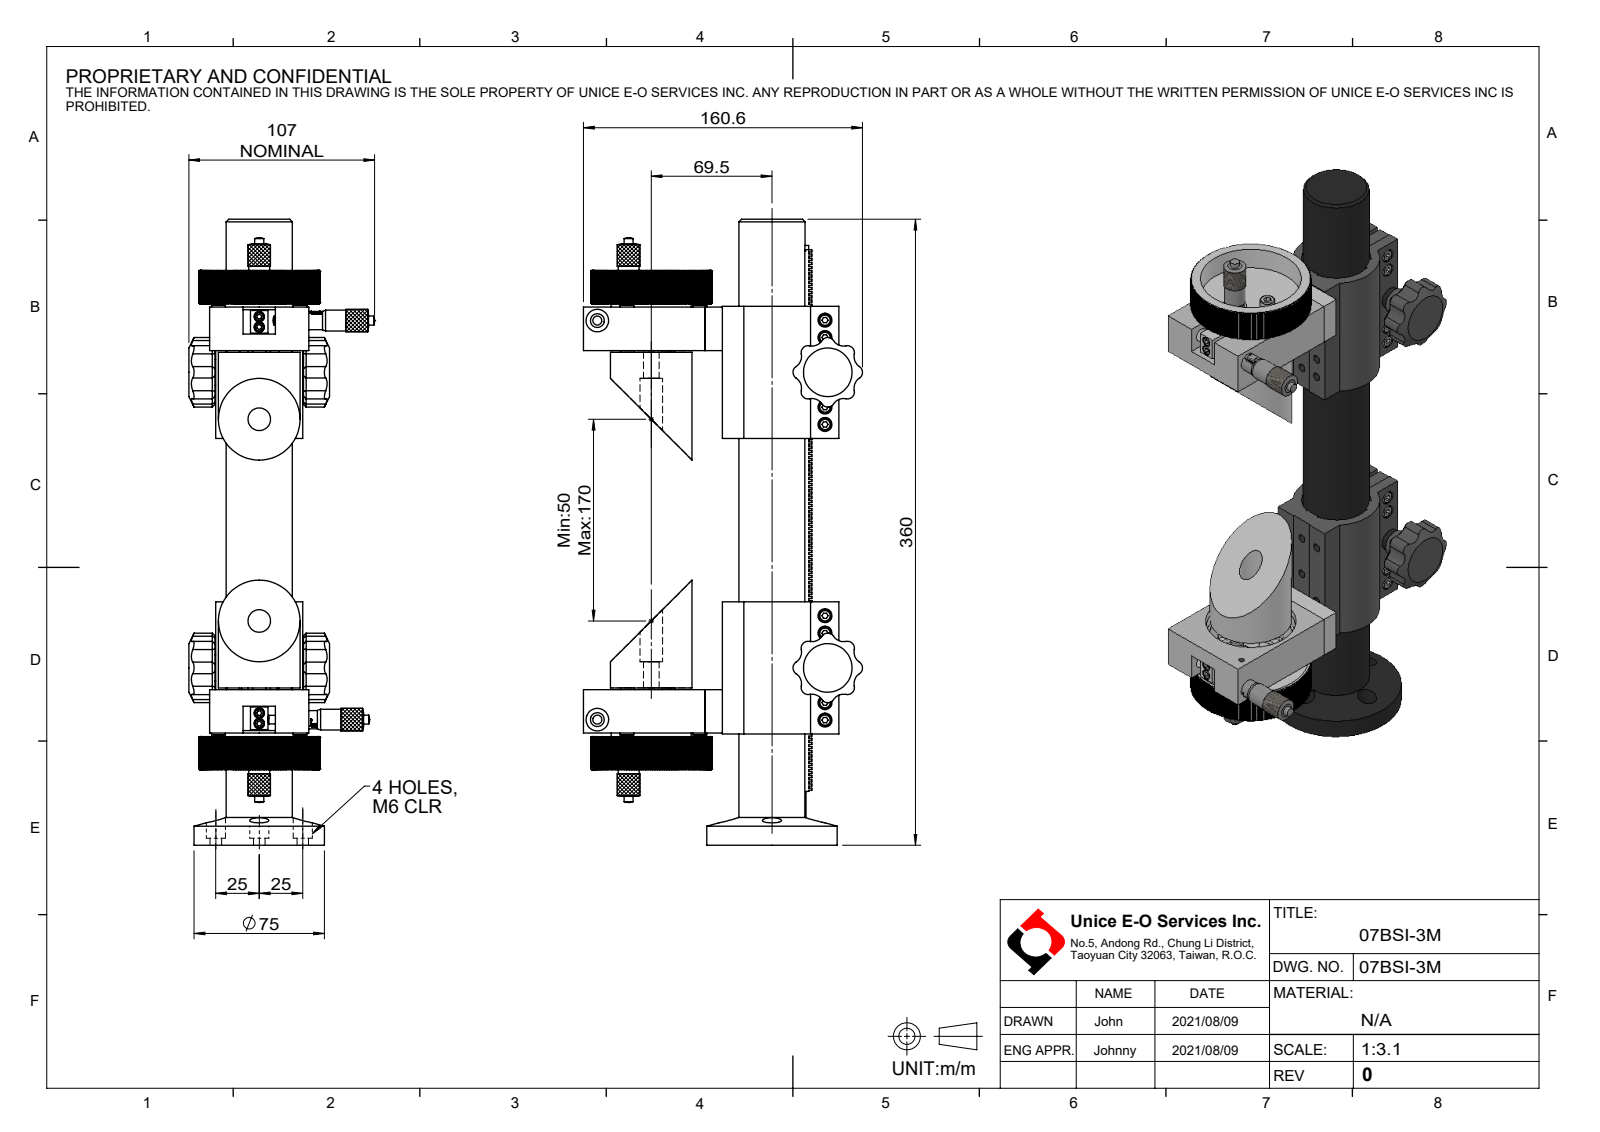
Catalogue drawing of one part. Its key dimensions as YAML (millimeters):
part_name: "07BSI-3M"
step_written_by: "SolidWorks 2020 (CONFIG_CONTROL_DESIGN)"
units: millimeters
bodies: {solids: 0, faces: 2169, planar: 990, cylindrical: 624, other: 555}
overall_size: [360, 160.6, 106.9]
round_holes:
  - {diameter: 8, count: 14}
  - {diameter: 5, count: 12}
  - {diameter: 11, count: 5}
  - {diameter: 6, count: 4}
  - {diameter: 6.6, count: 4}
  - {diameter: 2.5, count: 2}
  - {diameter: 9.6, count: 2}
  - {diameter: 10.6, count: 2}
  - {diameter: 3.3, count: 1}
  - {diameter: 13, count: 1}
  - {diameter: 14.5, count: 1}
  - {diameter: 52, count: 1}
round_bosses_or_shafts:
  - {diameter: 7, count: 6}
  - {diameter: 13, count: 3}
  - {diameter: 12, count: 3}
  - {diameter: 10.5, count: 3}
  - {diameter: 5.2, count: 3}
  - {diameter: 15, count: 2}
  - {diameter: 14.5, count: 2}
  - {diameter: 12.7, count: 2}
partial_cylinders:
  - {radius: 4, count: 16}
  - {radius: 7, count: 16}
  - {radius: 8.25, count: 2}
  - {radius: 10.15, count: 2}
  - {radius: 2.5, count: 1}
  - {radius: 20, count: 1}
  - {radius: 25, count: 1}
  - {radius: 34.75, count: 1}
face_to_face_distances: [3, 14, 7.5, 228, 16.5, 30, 6.5, 8, 30.5, 23.5]
hole_center_spacings: [25, 170, 12.5, 17.68, 27.95, 50, 120, 10]
